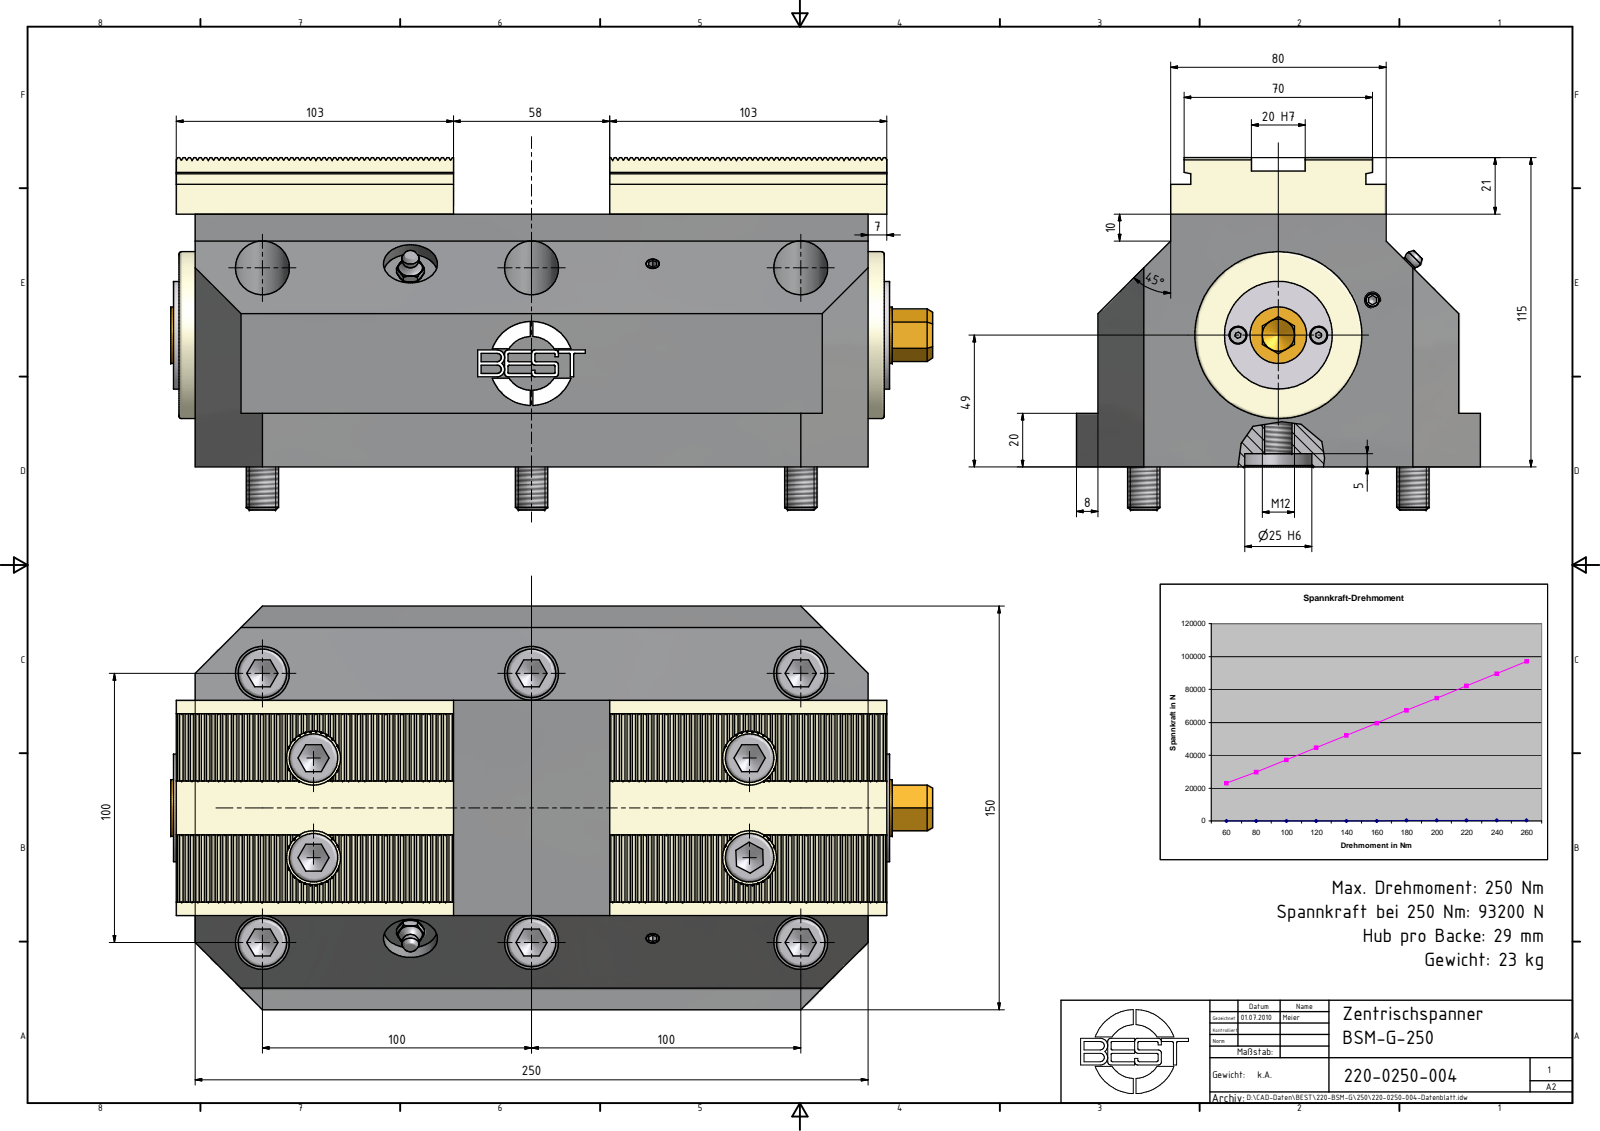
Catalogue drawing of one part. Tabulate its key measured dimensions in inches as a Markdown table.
| quantity | value |
| --- | --- |
| part name | 220-0250-004-Kunde |
| STEP written by | Autodesk Inventor 2010 (CONFIG_CONTROL_DESIGN) |
| units | inches |
| bodies | 1 solid, 246 faces (127 planar, 22 cylindrical, 97 other) |
| overall size | 11.142 × 5.906 × 5.157 |
| volume | 192.6 in³ |
| surface area | 313.9 in² |
| round bosses / shafts (diameter × count) | 0.709 × 6, 0.472 × 6, 3.15 × 1, 2.441 × 1, 1.575 × 1, 0.827 × 1, 0.157 × 1 |
| partial cylindrical surfaces (radius × count) | 0.472 × 1 |
| main face-to-face distances | 4.528, 0.315, 1.063, 4.213, 1.378, 5.591, 5.276, 0.197, 9.843, 4.331 |
